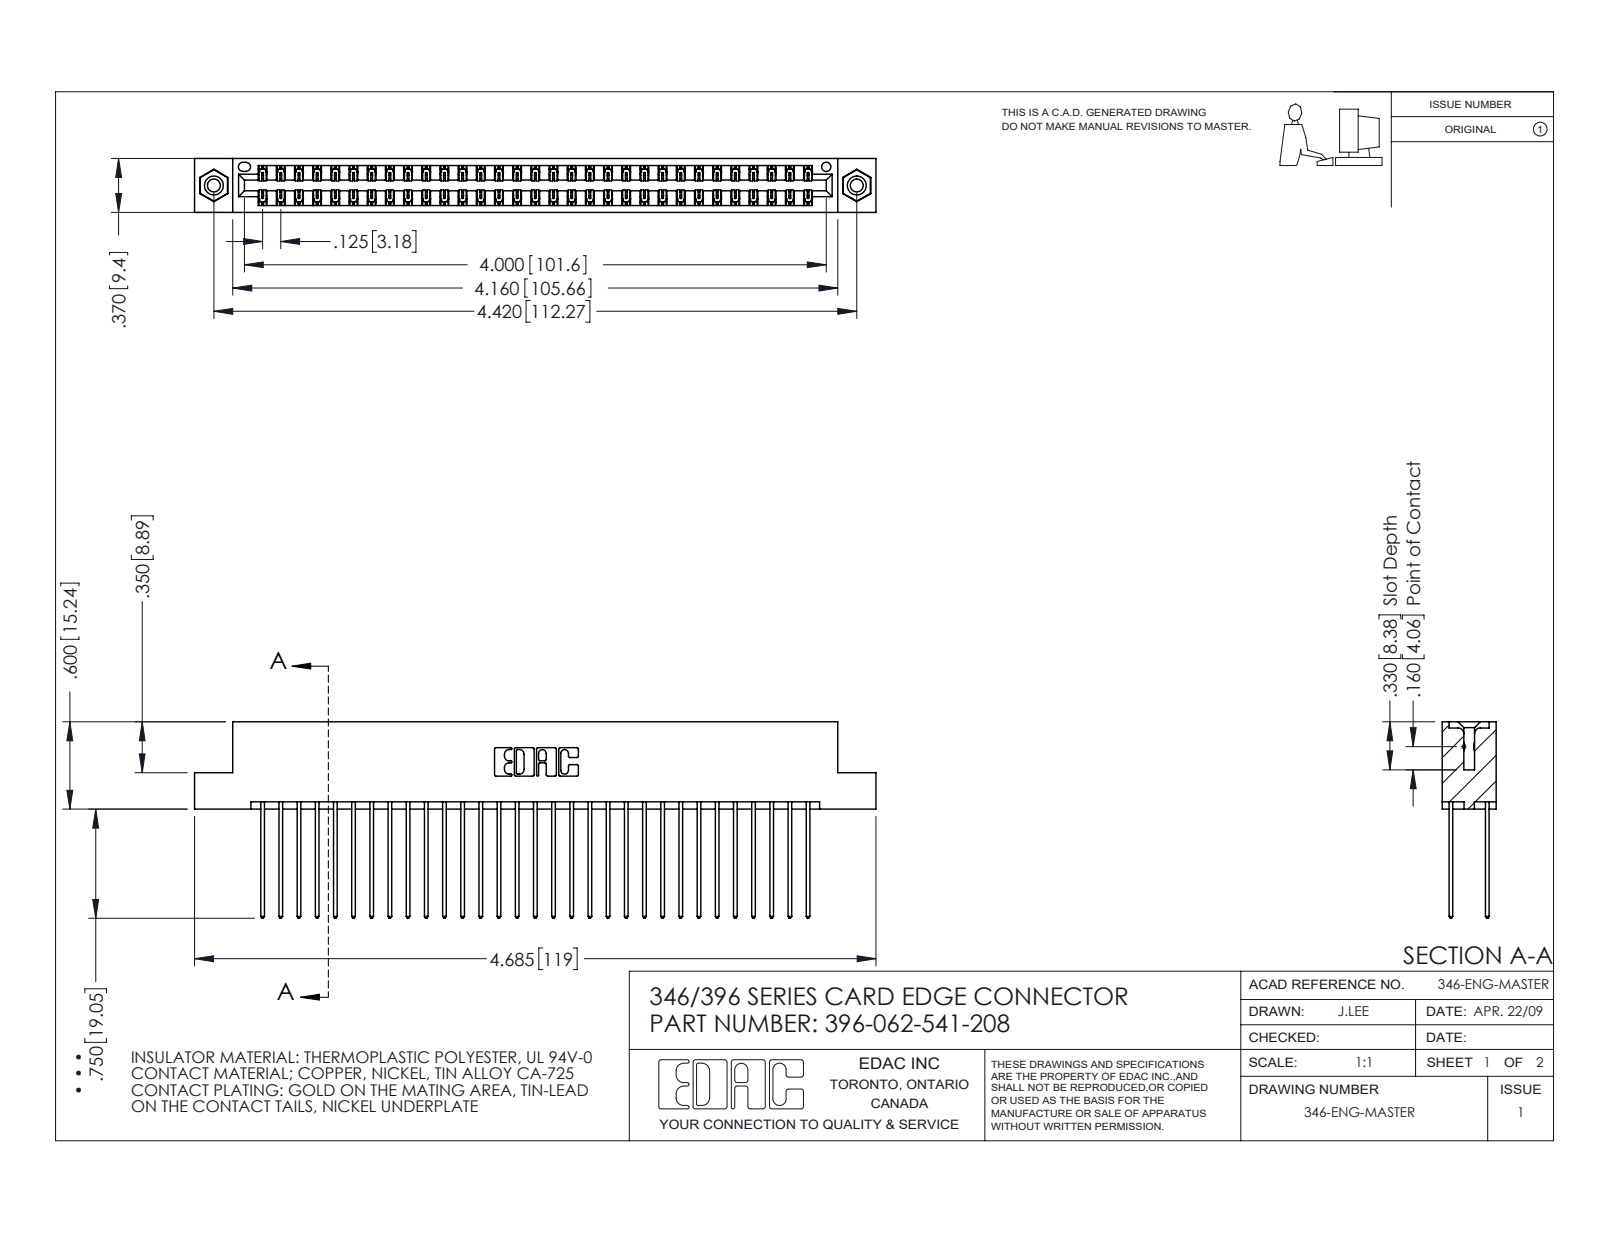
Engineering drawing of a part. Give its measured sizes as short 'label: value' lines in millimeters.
name: 346 Part_Flush Mounting Lugs - 0.156 Dia-TI; 345-250-001_345-250-003-102; 345-292-001_345-293-141; 396-062-541-208
written by: SolidWorks 2016 (CONFIG_CONTROL_DESIGN)
unit: mm
bodies: 65 solids, 3406 faces (2278 planar, 1112 cylindrical, 16 other)
size: 119 × 34.3 × 9.4
volume: 11 900 mm³; area: 17 860 mm²
holes: 2× ⌀2.3, 2× ⌀3.2, 2× ⌀4, 1× ⌀1.6
bosses: 2× ⌀3.9
rounds: 93× R0.2, 62× R0.3, 22× R0.3, 6× R0.2, 6× R0.8, 3× R0.7, 2× R0.4, 2× R0.6
face distances: 1.2, 8.2, 6.4, 1.8, 7.6, 0.6, 9.4, 7, 5.7, 3.8
hole spacings: 6.2, 107, 112.3
